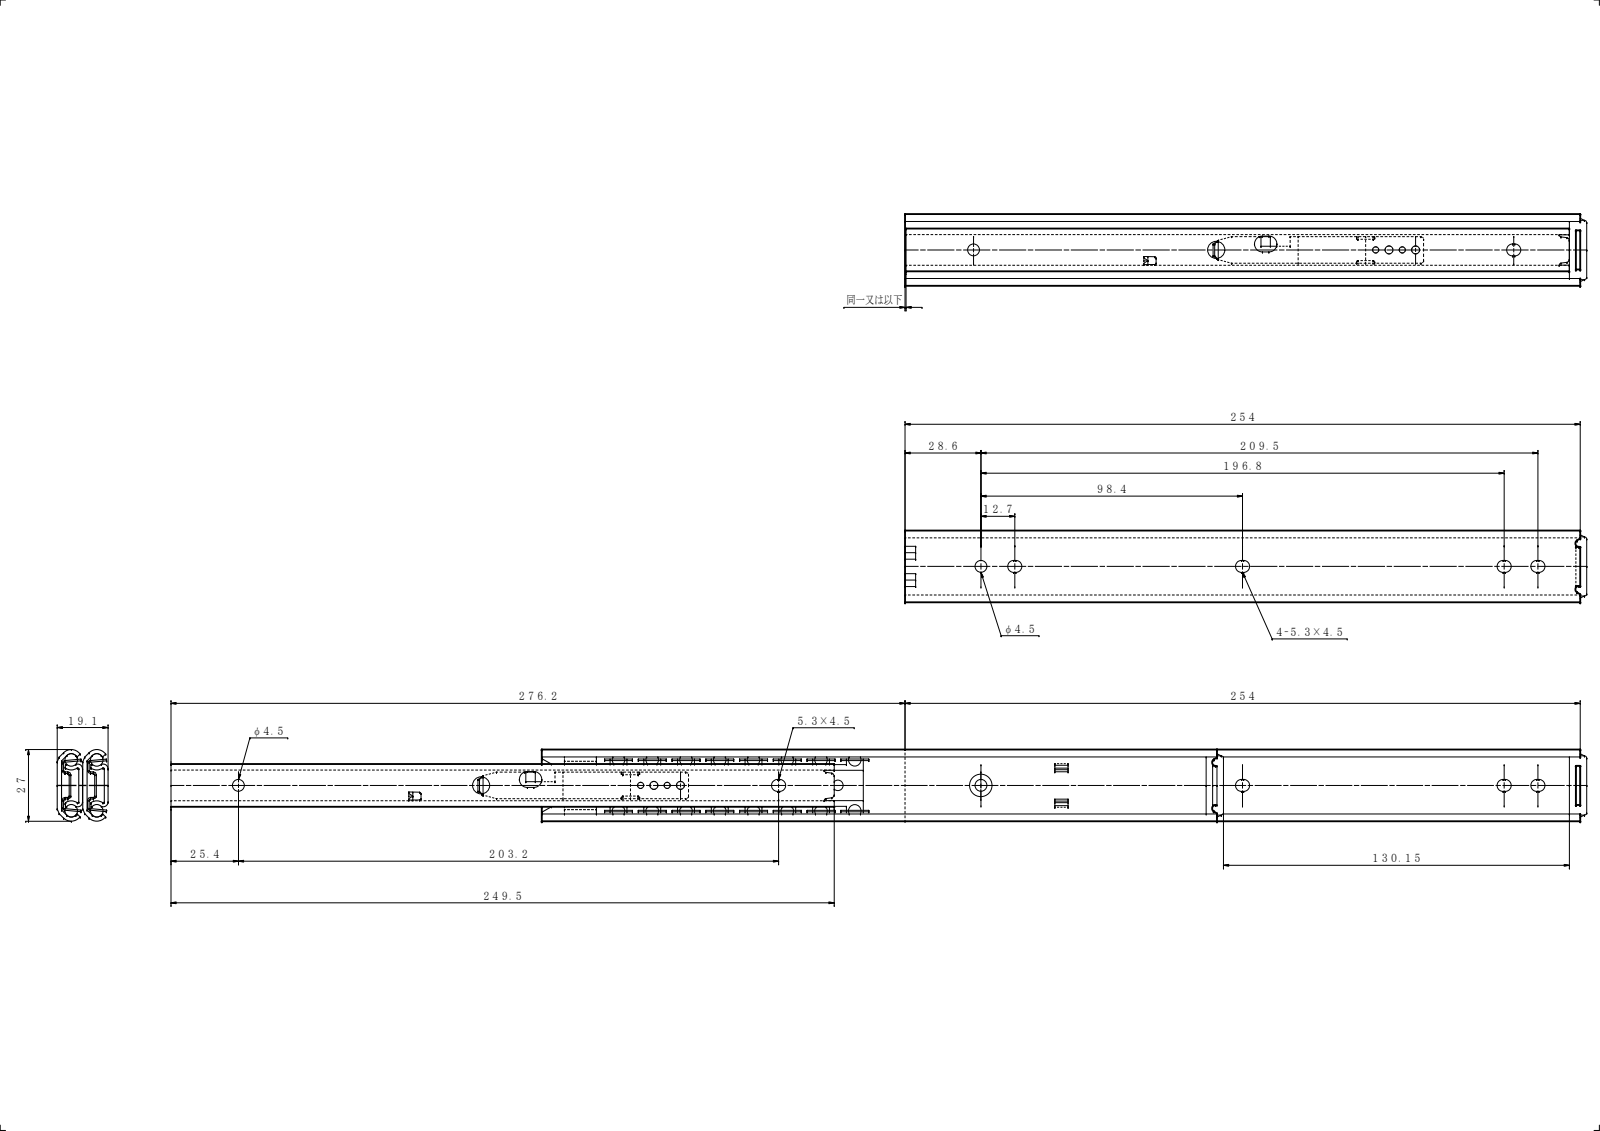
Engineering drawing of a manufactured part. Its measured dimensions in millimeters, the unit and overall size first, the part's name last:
Units: millimetres
Overall size (bounding box): 532.6 × 27 × 19
Round holes (diameter × count): ⌀2.34 ×2, ⌀2.9 ×2, ⌀3.03 ×2, ⌀4.5 ×2, ⌀4 ×1, ⌀4.2 ×1, ⌀4.3 ×1, ⌀6.5 ×1, ⌀8.5 ×1
Round bosses / shafts (diameter × count): ⌀4.5 ×2, ⌀4.3 ×2, ⌀4.25 ×2, ⌀3.9 ×2
Partial cylindrical surfaces — rounded edges, fillets, slot ends (radius × count): R0.2 ×26, R2 ×23, R1 ×10, R2.25 ×10, R3 ×8, R0.28 ×4, R0.5 ×4, R1.68 ×4
Main face-to-face distances: 9.5, 1.6, 7.9, 6.5, 1.4, 8.1, 11.1, 17.6, 16, 19
Hole centre spacings: 5, 10, 15, 22.75, 25.2, 25.25, 27.65, 32.58
Volume: 48 303 mm³ · Surface area: 68 289 mm²
Bodies: 8 solids, 360 faces (158 planar, 182 cylindrical, 20 other)
Part name (STEP PRODUCT): 2736-10; SBP806 リードイン; IM-A 2736-10; OM-A 2736-10 (+4 more)
STEP written by: SolidWorks 2019 (CONFIG_CONTROL_DESIGN)
